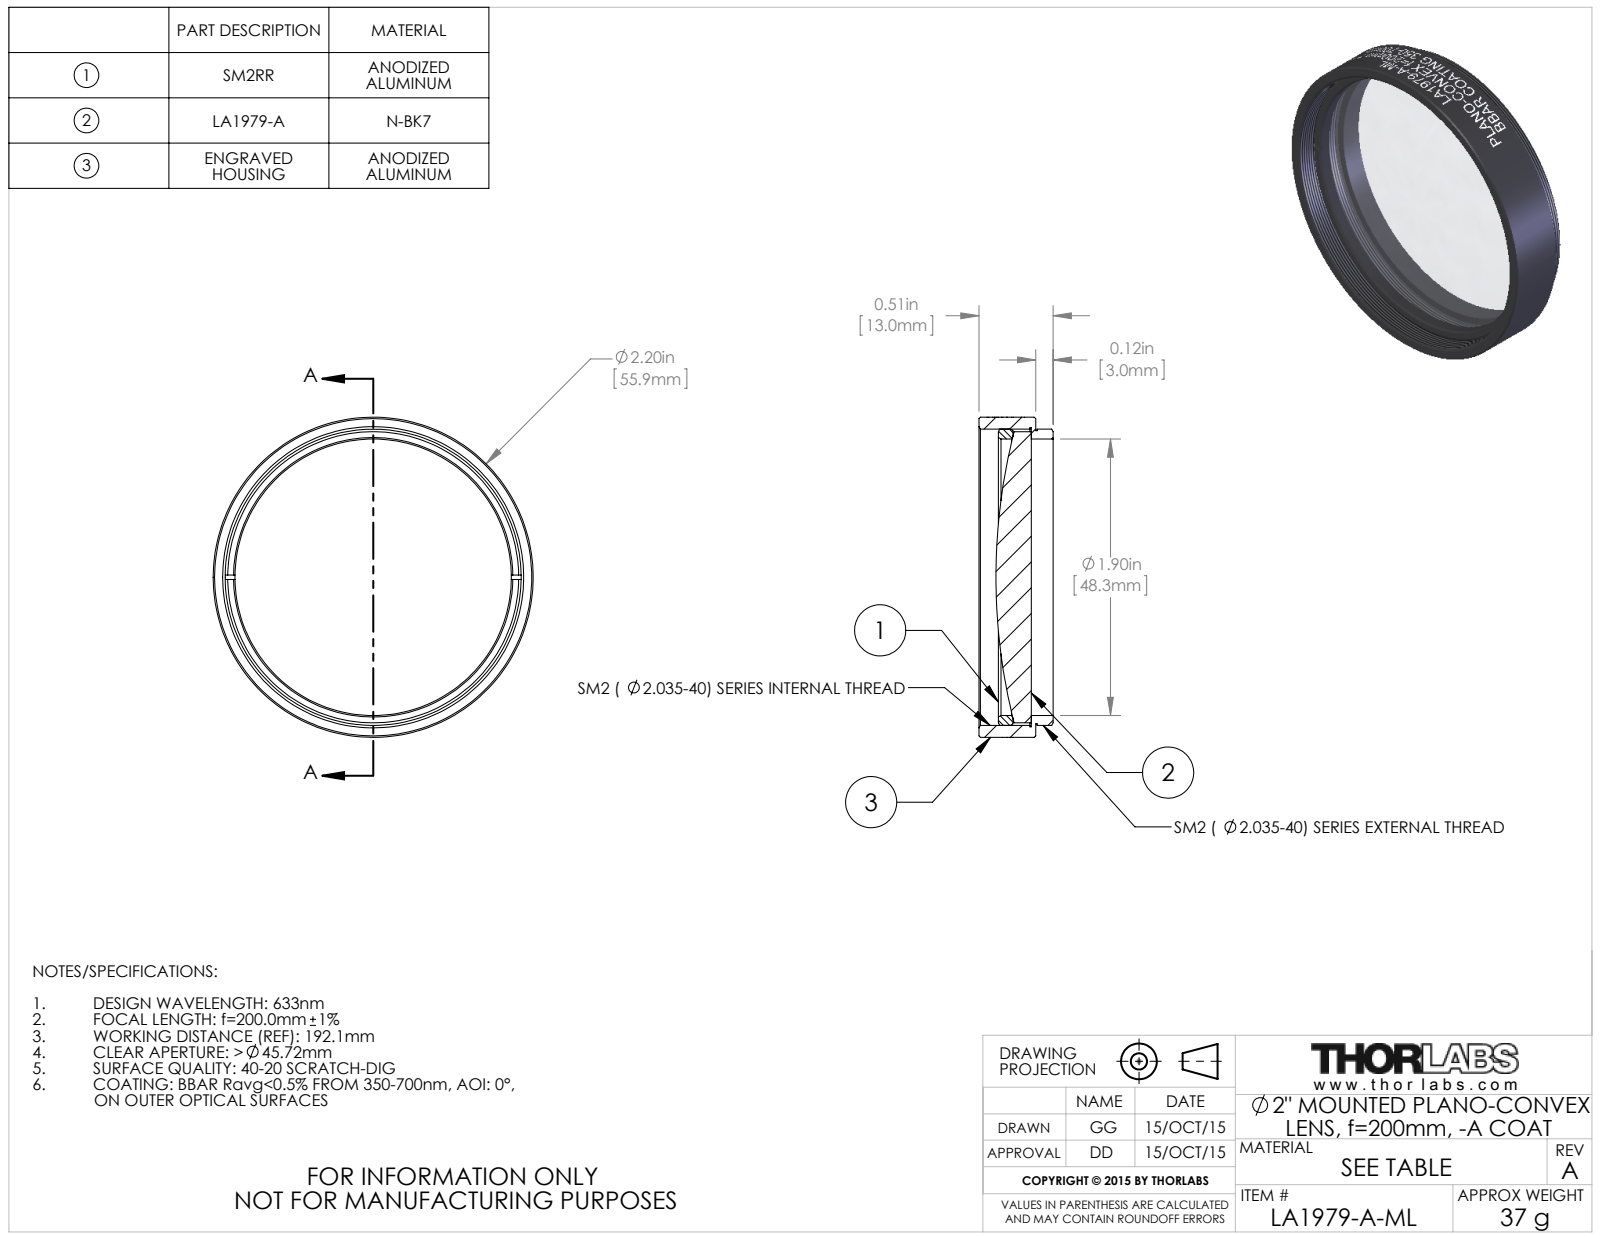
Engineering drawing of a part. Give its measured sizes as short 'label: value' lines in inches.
name: TTN039669-E0W
written by: SolidWorks 2014 (CONFIG_CONTROL_DESIGN)
unit: in
bodies: 3 solids, 143 faces (16 planar, 107 cylindrical, 20 other)
size: 2.2 × 2.2 × 0.51
volume: 0.882 in³; area: 17.64 in²
holes: 1× ⌀1.9, 1× ⌀2.055
bosses: 1× ⌀2.2, 1× ⌀2.035, 1× ⌀2.015, 1× ⌀2
face distances: 0.03, 0.39, 0.36, 0.12, 0.15, 0.51, 0.276, 0.156, 0.126, 0.234
